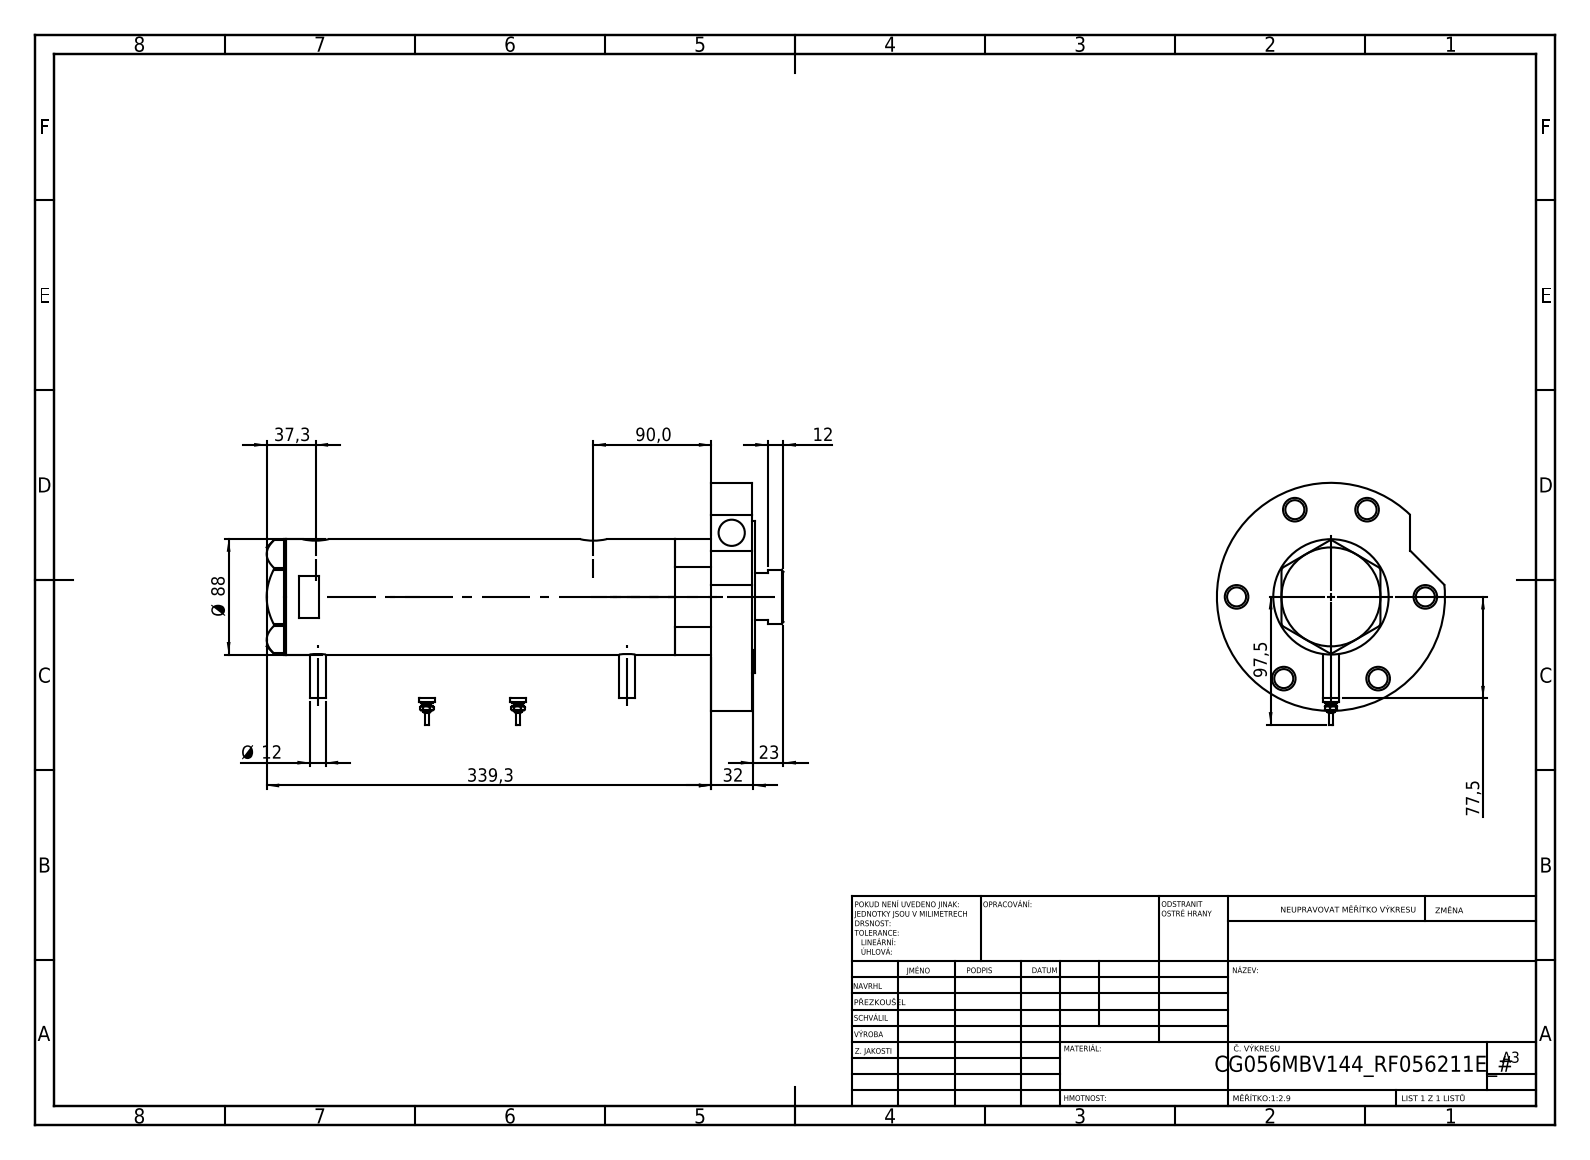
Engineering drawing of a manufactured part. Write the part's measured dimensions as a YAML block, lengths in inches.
part_name: "Switch; V270CG_VC; V270CG_BACK; V270CG_FRONT (+2 more)"
step_written_by: "SolidWorks 2019 (CONFIG_CONTROL_DESIGN)"
units: inches
bodies: {solids: 7, faces: 257, planar: 91, cylindrical: 102, other: 64}
overall_size: [15.524, 7.264, 6.85]
volume: 156.6
surface_area: 559.5
round_holes:
  - {diameter: 0.571, count: 7}
  - {diameter: 0.709, count: 6}
  - {diameter: 0.787, count: 3}
  - {diameter: 0.492, count: 2}
  - {diameter: 0.518, count: 2}
  - {diameter: 1.654, count: 1}
  - {diameter: 1.713, count: 1}
  - {diameter: 2.205, count: 1}
  - {diameter: 2.362, count: 1}
  - {diameter: 2.953, count: 1}
  - {diameter: 3.15, count: 1}
round_bosses_or_shafts:
  - {diameter: 0.472, count: 4}
  - {diameter: 0.354, count: 2}
  - {diameter: 0.276, count: 2}
  - {diameter: 0.177, count: 2}
  - {diameter: 0.098, count: 2}
  - {diameter: 6.85, count: 1}
  - {diameter: 4.567, count: 1}
  - {diameter: 3.465, count: 1}
face_to_face_distances: [1.22, 0.079, 14.067, 12.768, 13.988, 1.299, 9.228, 3.539, 4.76, 4.839]
hole_center_spacings: [2.835, 3.15, 4.714, 4.91, 5.085, 5.657, 0.067, 1.016]
